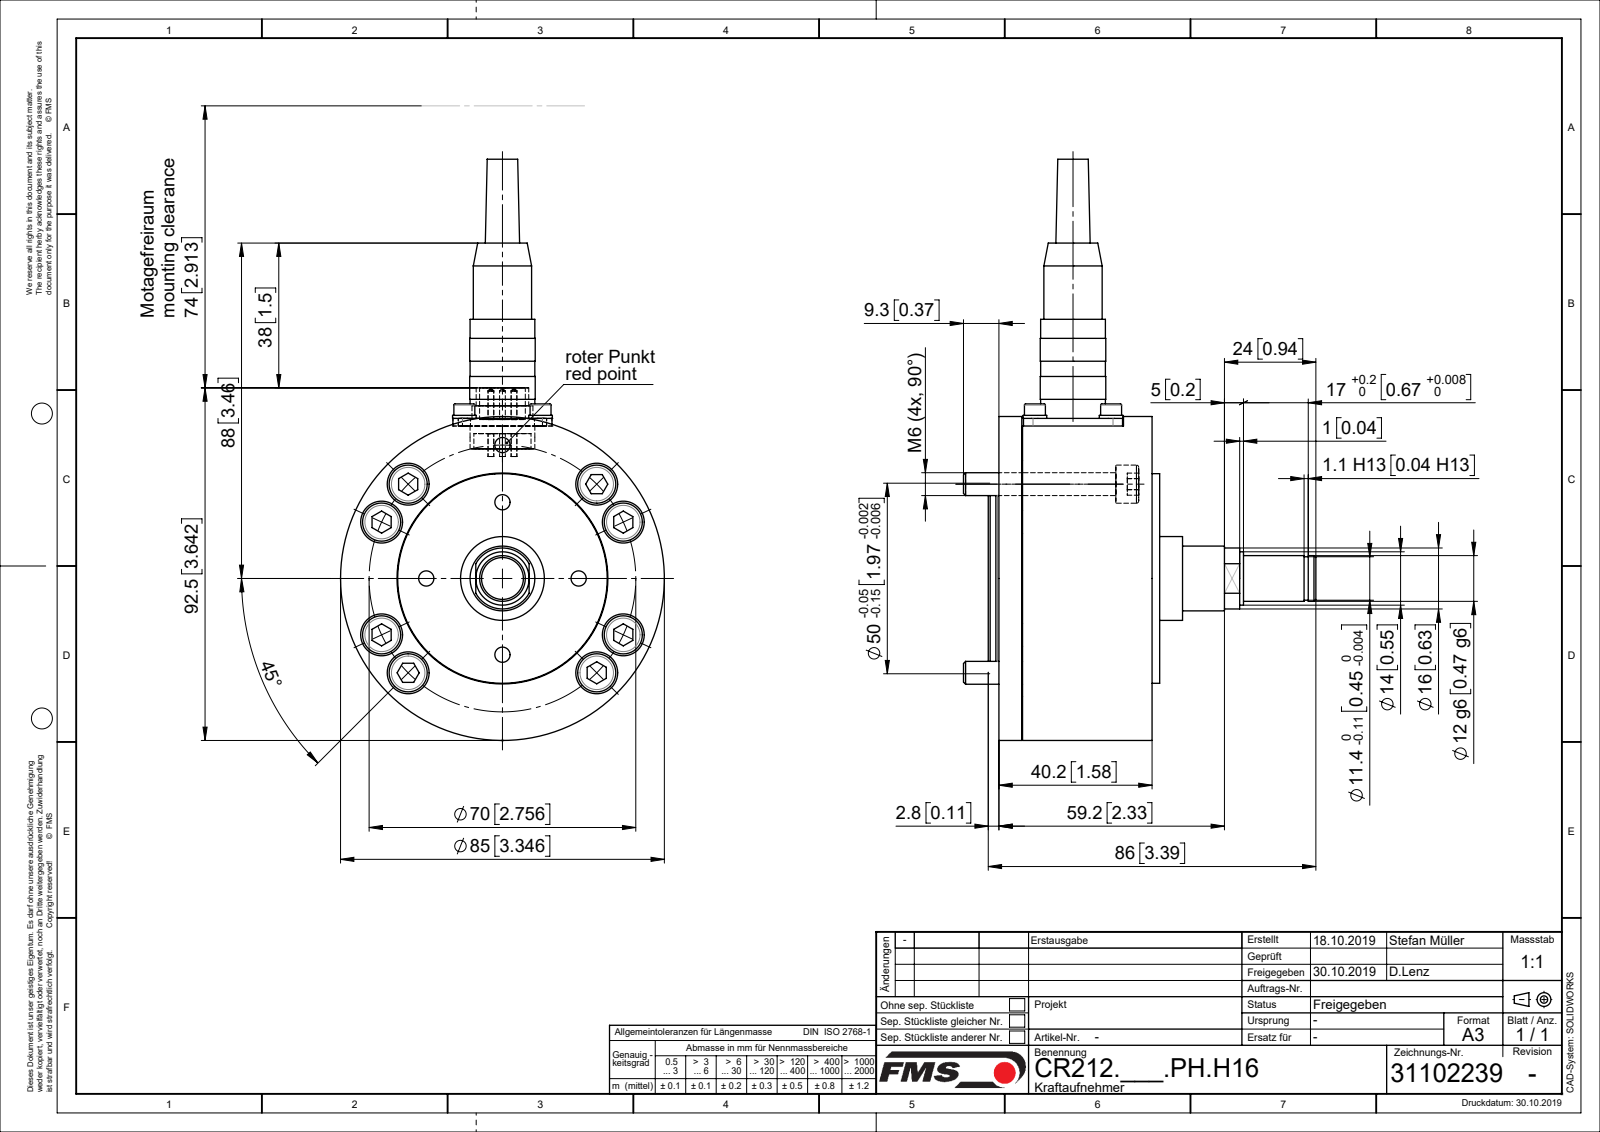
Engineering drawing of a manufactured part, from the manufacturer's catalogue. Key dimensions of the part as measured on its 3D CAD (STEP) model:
Part name (STEP PRODUCT): 31102229_STP; C0709081; C0612056; C0709072 (+8 more)
STEP written by: Mechanical Desktop 2009 (CONFIG_CONTROL_DESIGN)
Units: millimetres
Bodies: 26 solids, 521 faces (180 planar, 243 cylindrical, 98 other)
Overall size (bounding box): 152.5 × 92.5 × 85
Volume: 231 287 mm³ · Surface area: 73 181 mm²
Round holes (diameter × count): ⌀6.5 ×8, ⌀11 ×8, ⌀2.6 ×4, ⌀3.2 ×4, ⌀4 ×4, ⌀5.15 ×4, ⌀7 ×4, ⌀7.15 ×1, ⌀10.68 ×1, ⌀12 ×1, ⌀15 ×1, ⌀18 ×1
Round bosses / shafts (diameter × count): ⌀10 ×8, ⌀6 ×8, ⌀1.5 ×5, ⌀6.2 ×4, ⌀5.5 ×4, ⌀5 ×4, ⌀3 ×4, ⌀17 ×2
Partial cylindrical surfaces — rounded edges, fillets, slot ends (radius × count): R2.5 ×4, R5 ×2, R8 ×1
Main face-to-face distances: 6, 6.3, 2, 2.7, 34, 40.3, 34.3, 45, 3, 42.3
Hole centre spacings: 20, 25.2, 35, 51.14, 28.28, 12.16, 14.14, 18.87
